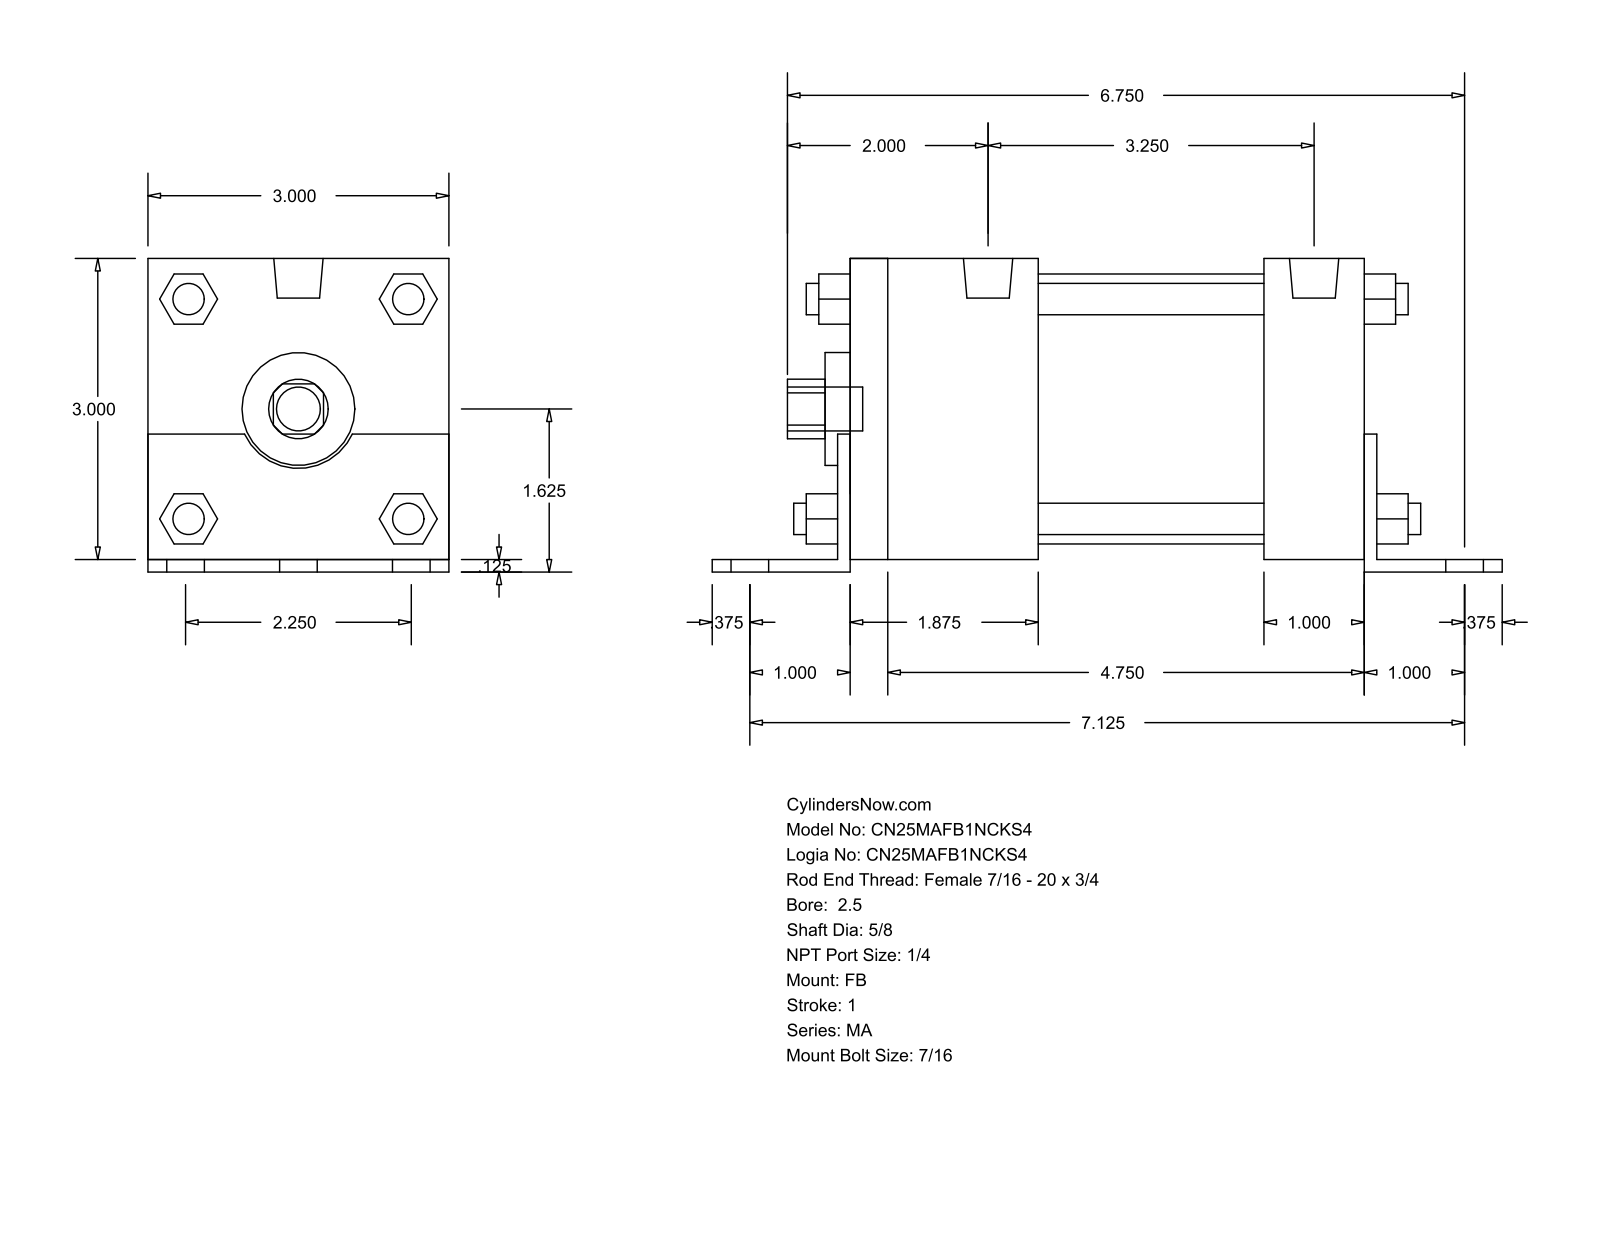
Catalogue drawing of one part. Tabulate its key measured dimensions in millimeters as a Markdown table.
| quantity | value |
| --- | --- |
| part name | MA_FB__0250_0.625 |
| STEP written by | GSSL Pune (CONFIG_CONTROL_DESIGN) |
| units | millimeters |
| bodies | 0 solids, 140 faces (105 planar, 35 cylindrical, 0 other) |
| overall size | 200.03 × 79.38 × 76.2 |
| round holes (diameter × count) | 15.88 × 1, 28.57 × 1, 68.33 × 1 |
| round bosses / shafts (diameter × count) | 7.94 × 8, 11.11 × 7, 12.49 × 2 |
| partial cylindrical surfaces (radius × count) | 7.54 × 1, 15.05 × 1 |
| main face-to-face distances | 76.2, 3.17, 79.37, 130.17, 136.52, 3.18, 82.55, 133.34, 47.62, 25.4 |
